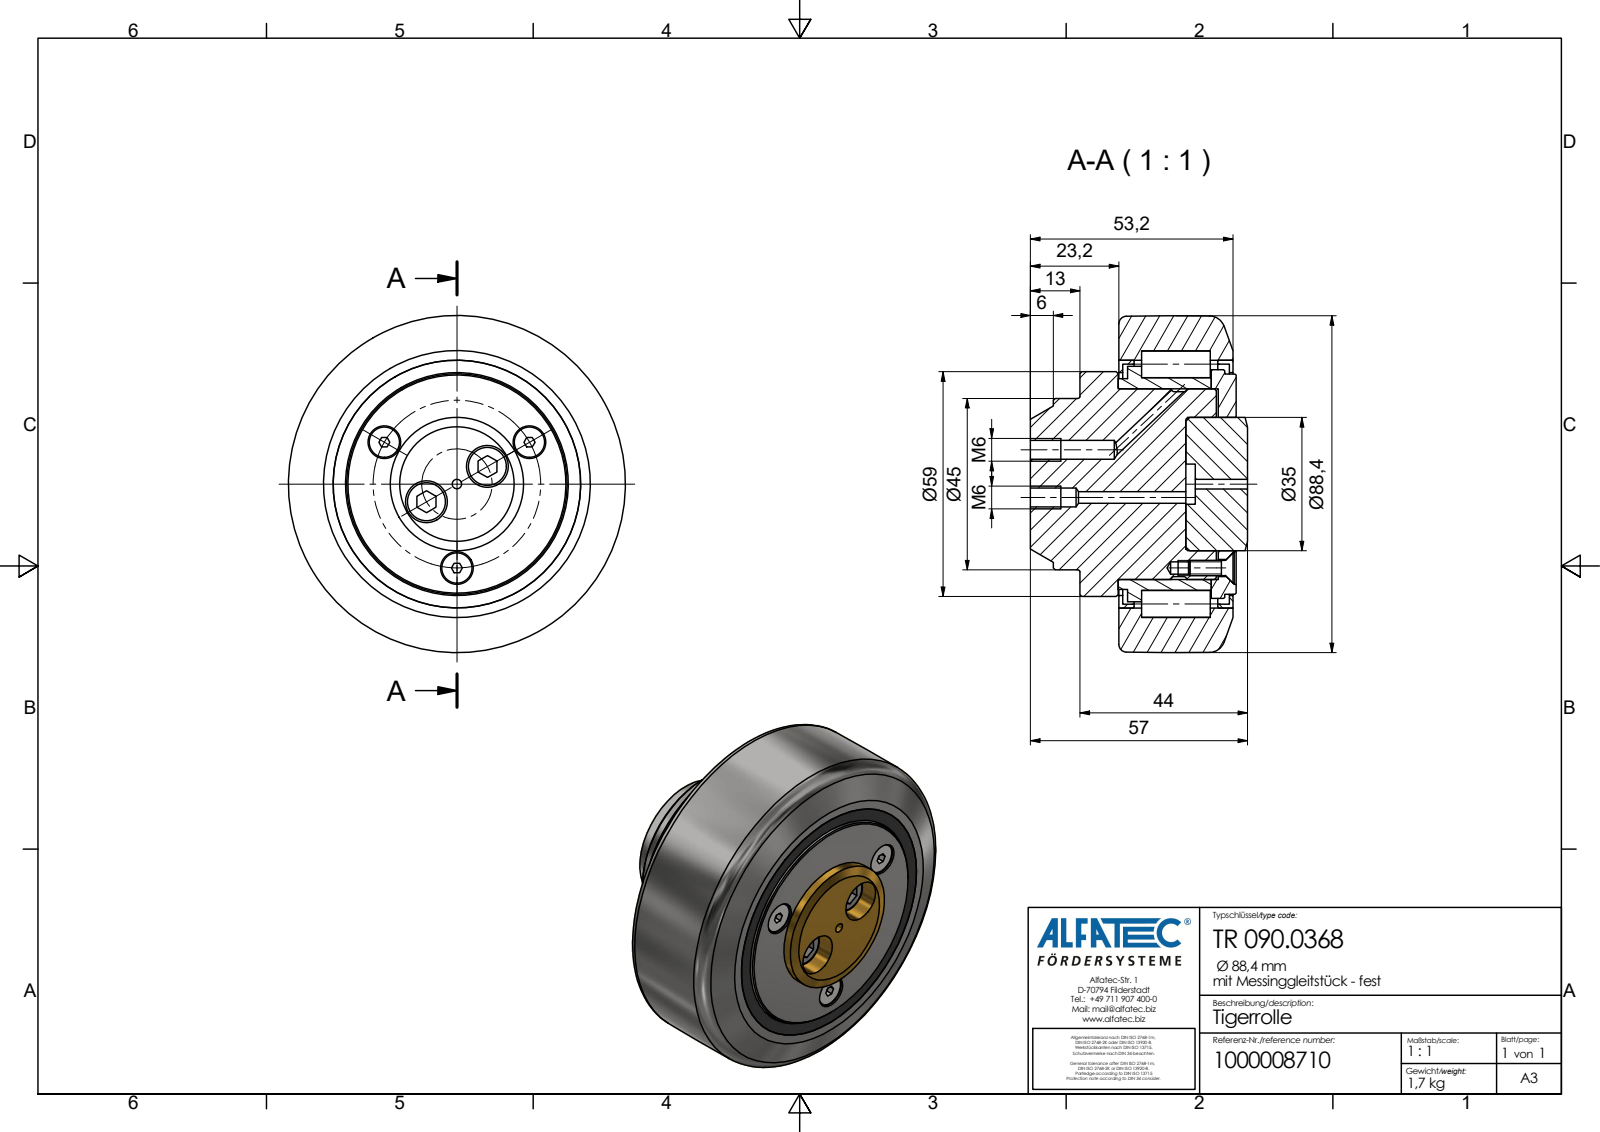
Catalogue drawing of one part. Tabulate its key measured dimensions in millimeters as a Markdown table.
| quantity | value |
| --- | --- |
| part name | TR 090.0368_Kontur |
| STEP written by | Autodesk Inventor 2020 (AP242_MANAGED_MODEL_BASED_3D_ENGINEERING_MIM_LF) |
| units | millimeters |
| bodies | 1 solid, 71 faces (37 planar, 18 cylindrical, 16 other) |
| overall size | 88.4 × 88.4 × 57 |
| volume | 228 095 mm³ |
| surface area | 24 488 mm² |
| round holes (diameter × count) | 8.6 × 3, 2.5 × 2, 4.92 × 2, 11 × 2, 3 × 1 |
| round bosses / shafts (diameter × count) | 8 × 3, 59 × 1, 57.8 × 1, 55.3 × 1, 45 × 1, 35 × 1 |
| main face-to-face distances | 30, 30.8, 0.8, 10.2, 40.2, 41, 13, 23.2, 53.2, 54 |
| hole center spacings | 22, 38.1, 9.25, 19.15, 23.94, 27.8, 3.5, 8.09 |
